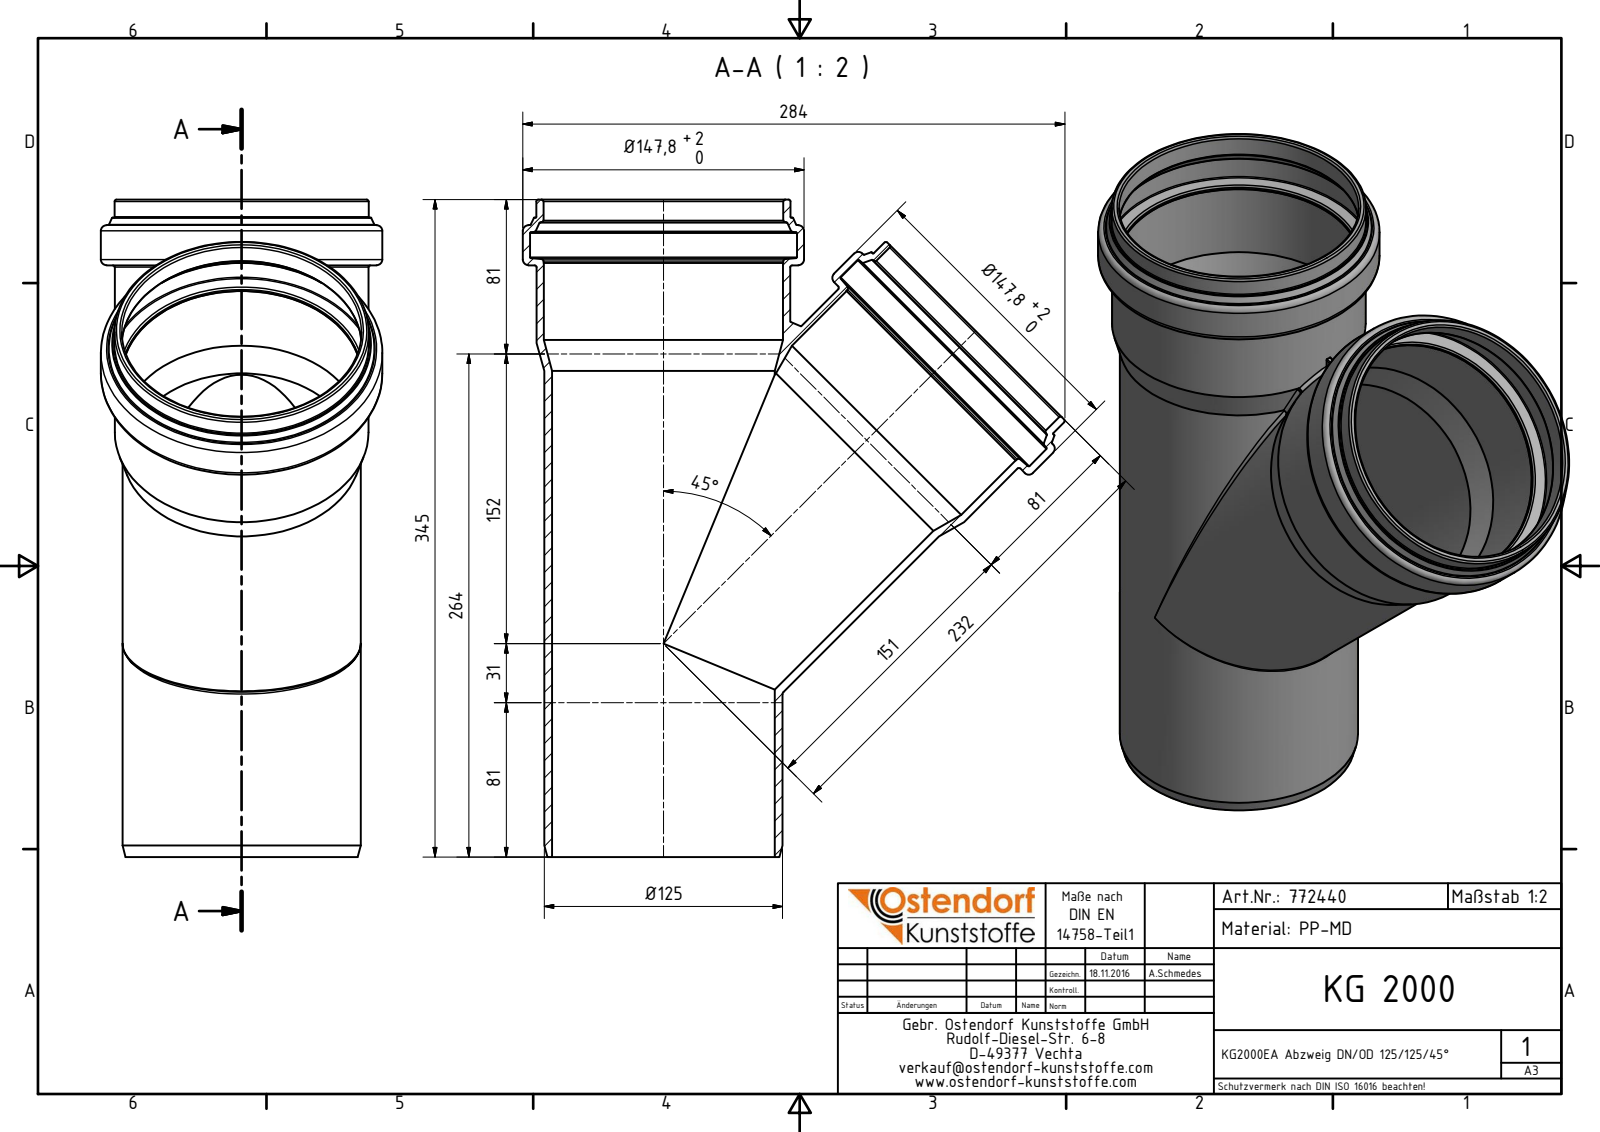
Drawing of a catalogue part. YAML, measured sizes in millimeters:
part_name: "772440 KG2000EA Abzweig DN_OD 125_125_45°"
step_written_by: "Autodesk Inventor 2016 (AUTOMOTIVE_DESIGN)"
units: millimeters
bodies: {solids: 1, faces: 86, planar: 14, cylindrical: 20, other: 52}
overall_size: [345, 284.73, 147.8]
volume: 767451
surface_area: 388407
round_holes:
  - {diameter: 125.9, count: 3}
  - {diameter: 116.9, count: 2}
  - {diameter: 125.6, count: 2}
  - {diameter: 140.2, count: 2}
round_bosses_or_shafts:
  - {diameter: 147.8, count: 2}
  - {diameter: 133.5, count: 2}
  - {diameter: 133.2, count: 2}
  - {diameter: 125.1, count: 2}
partial_cylinders:
  - {radius: 0.5, count: 2}
face_to_face_distances: [34.5, 310.5, 345, 21.1, 13.4, 25.02, 3.92, 9.48, 331.6, 335.52]
